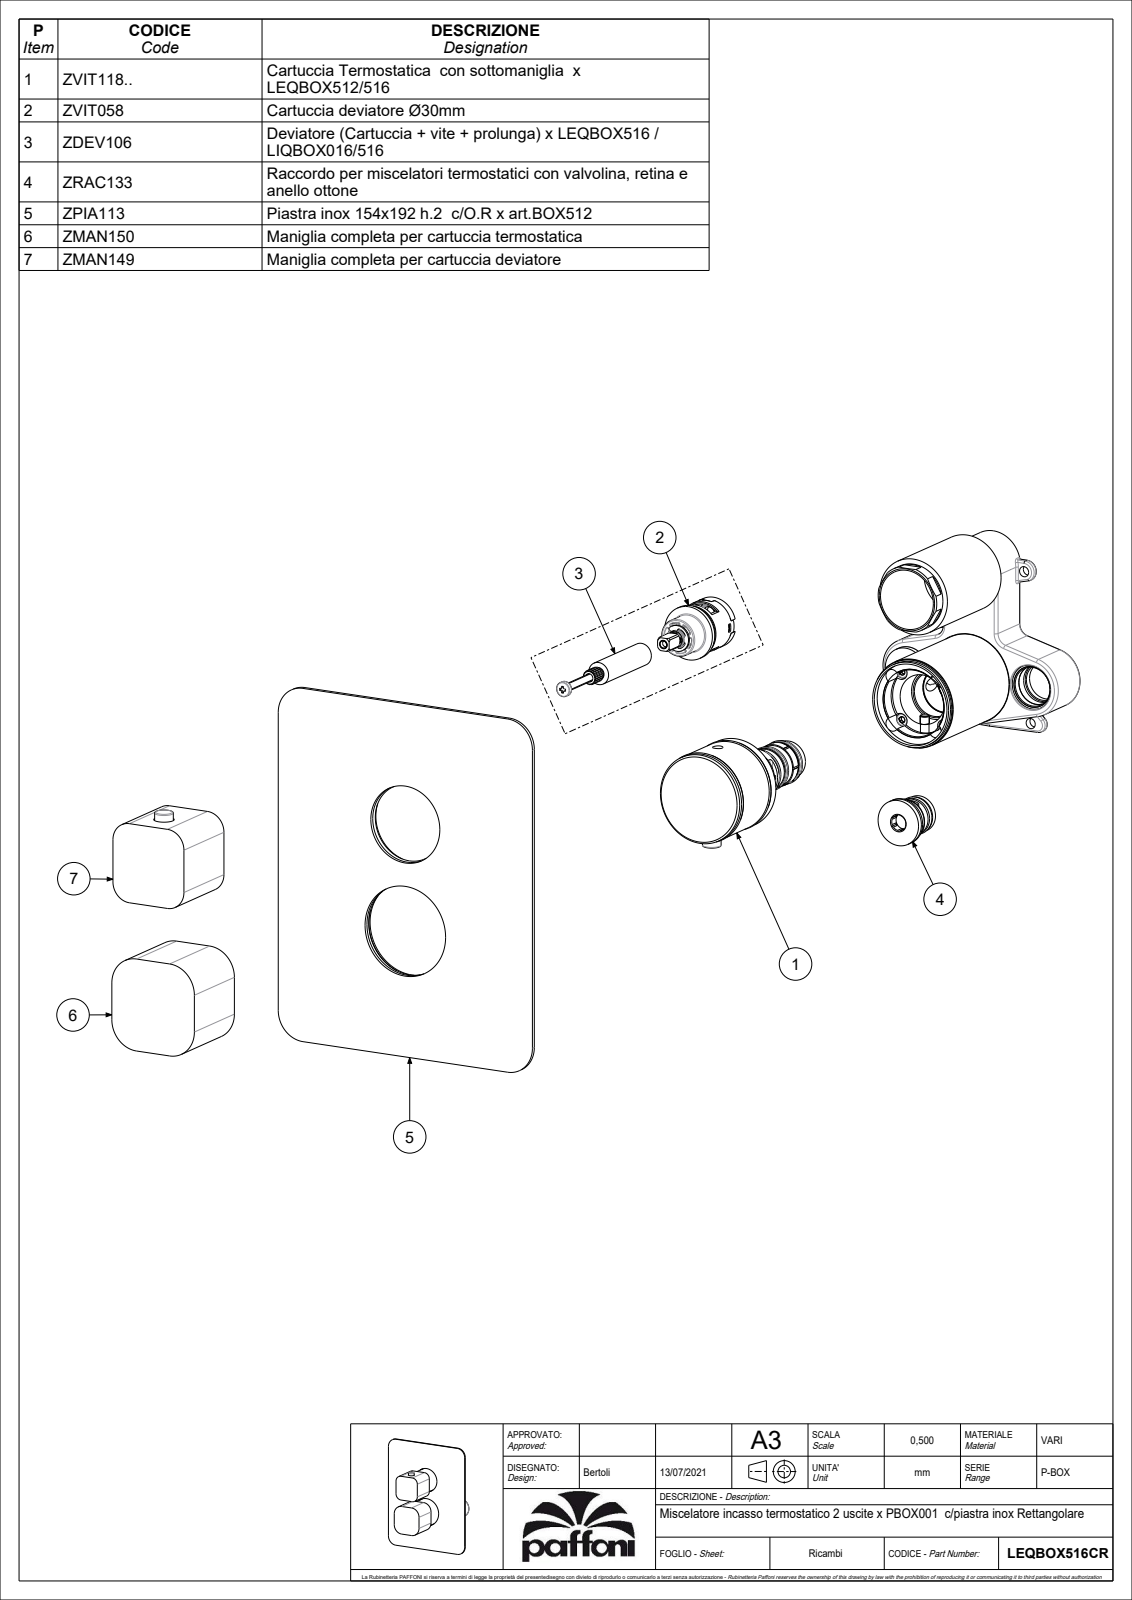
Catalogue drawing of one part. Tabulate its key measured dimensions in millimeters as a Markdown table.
| quantity | value |
| --- | --- |
| part name | LEQBOX516CR |
| STEP written by | CREO PARAMETRIC BY PTC INC, 2020044 (CONFIG_CONTROL_DESIGN) |
| units | millimeters |
| bodies | 6 solids, 1184 faces (486 planar, 372 cylindrical, 326 other) |
| overall size | 192 × 154 × 71.8 |
| volume | 222 938 mm³ |
| surface area | 134 273 mm² |
| round holes (diameter × count) | 7.5 × 5, 5 × 4, 4.2 × 3, 3.25 × 2, 4 × 2, 6.4 × 2, 10.1 × 2, 2.5 × 1, 3 × 1, 3.1 × 1, 3.2 × 1, 4.5 × 1 |
| round bosses / shafts (diameter × count) | 6.9 × 4, 3.9 × 4, 1 × 4, 9.8 × 2, 48 × 1, 47.5 × 1, 45.5 × 1, 41 × 1 |
| partial cylindrical surfaces (radius × count) | 0.2 × 35, 0.31 × 34, 0.5 × 12, 1 × 10, 15 × 8, 4.25 × 4, 10 × 4, 0.3 × 2 |
| main face-to-face distances | 2, 3, 71.7, 69.7, 66.8, 43, 66.7, 3.1, 3.5, 68.8 |
| hole center spacings | 18.38, 26, 13.12, 30.64, 36.77, 46.84, 62.37, 72.18 |
